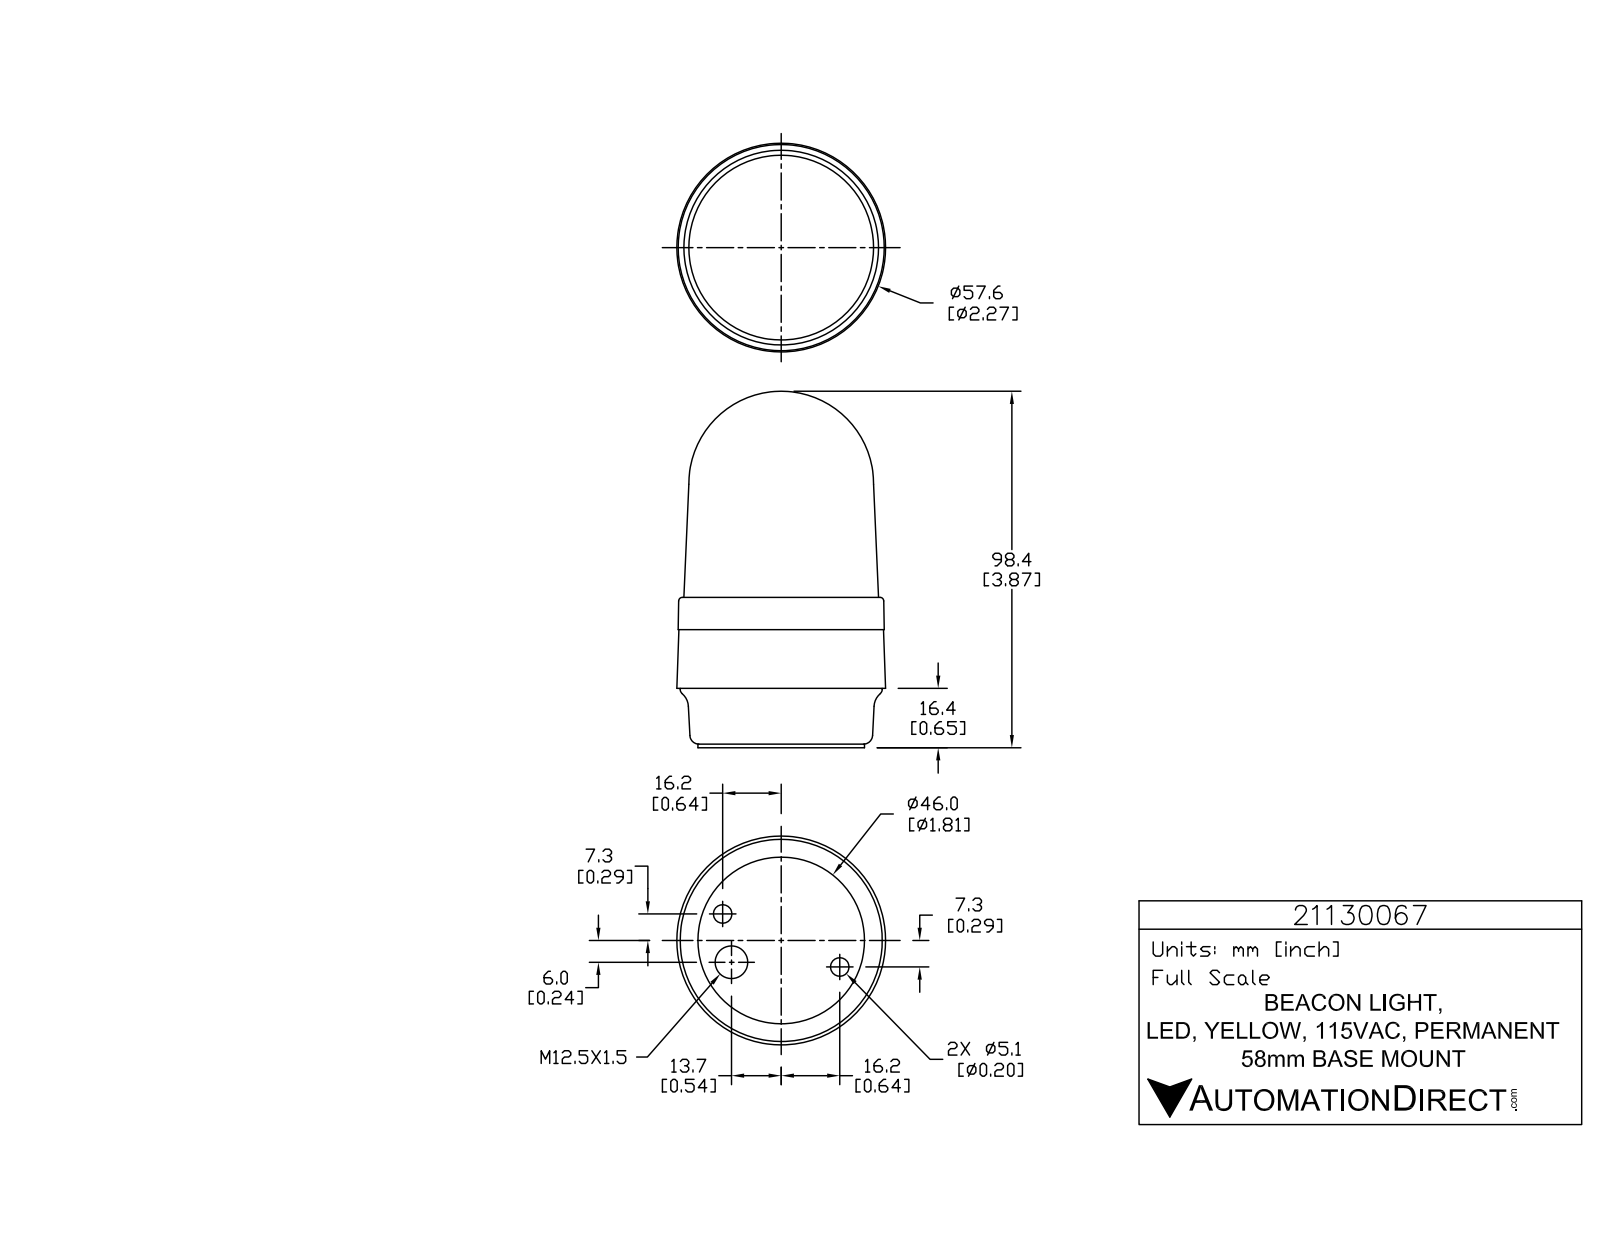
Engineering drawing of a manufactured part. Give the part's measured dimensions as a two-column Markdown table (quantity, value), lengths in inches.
| quantity | value |
| --- | --- |
| part name | 21130067 |
| STEP written by | SolidWorks 2015 (AUTOMOTIVE_DESIGN) |
| units | inches |
| bodies | 1 solid, 764 faces (527 planar, 145 cylindrical, 92 other) |
| overall size | 3.874 × 2.269 × 2.269 |
| volume | 12.2 in³ |
| surface area | 29.33 in² |
| round holes (diameter × count) | 0.039 × 3, 0.201 × 2, 0.354 × 1 |
| round bosses / shafts (diameter × count) | 0.226 × 3, 0.056 × 3, 2.197 × 1, 1.811 × 1 |
| partial cylindrical surfaces (radius × count) | 0.008 × 6, 0.008 × 6, 0.008 × 6, 0.131 × 6, 0.004 × 3, 0.005 × 3, 0.007 × 3, 0.008 × 3 |
| main face-to-face distances | 0.646, 0.039, 0.606, 1.634, 1.594, 0.988, 1.283, 1.244, 0.638, 0.35 |
| hole center spacings | 0.534, 1.179, 1.398 |
